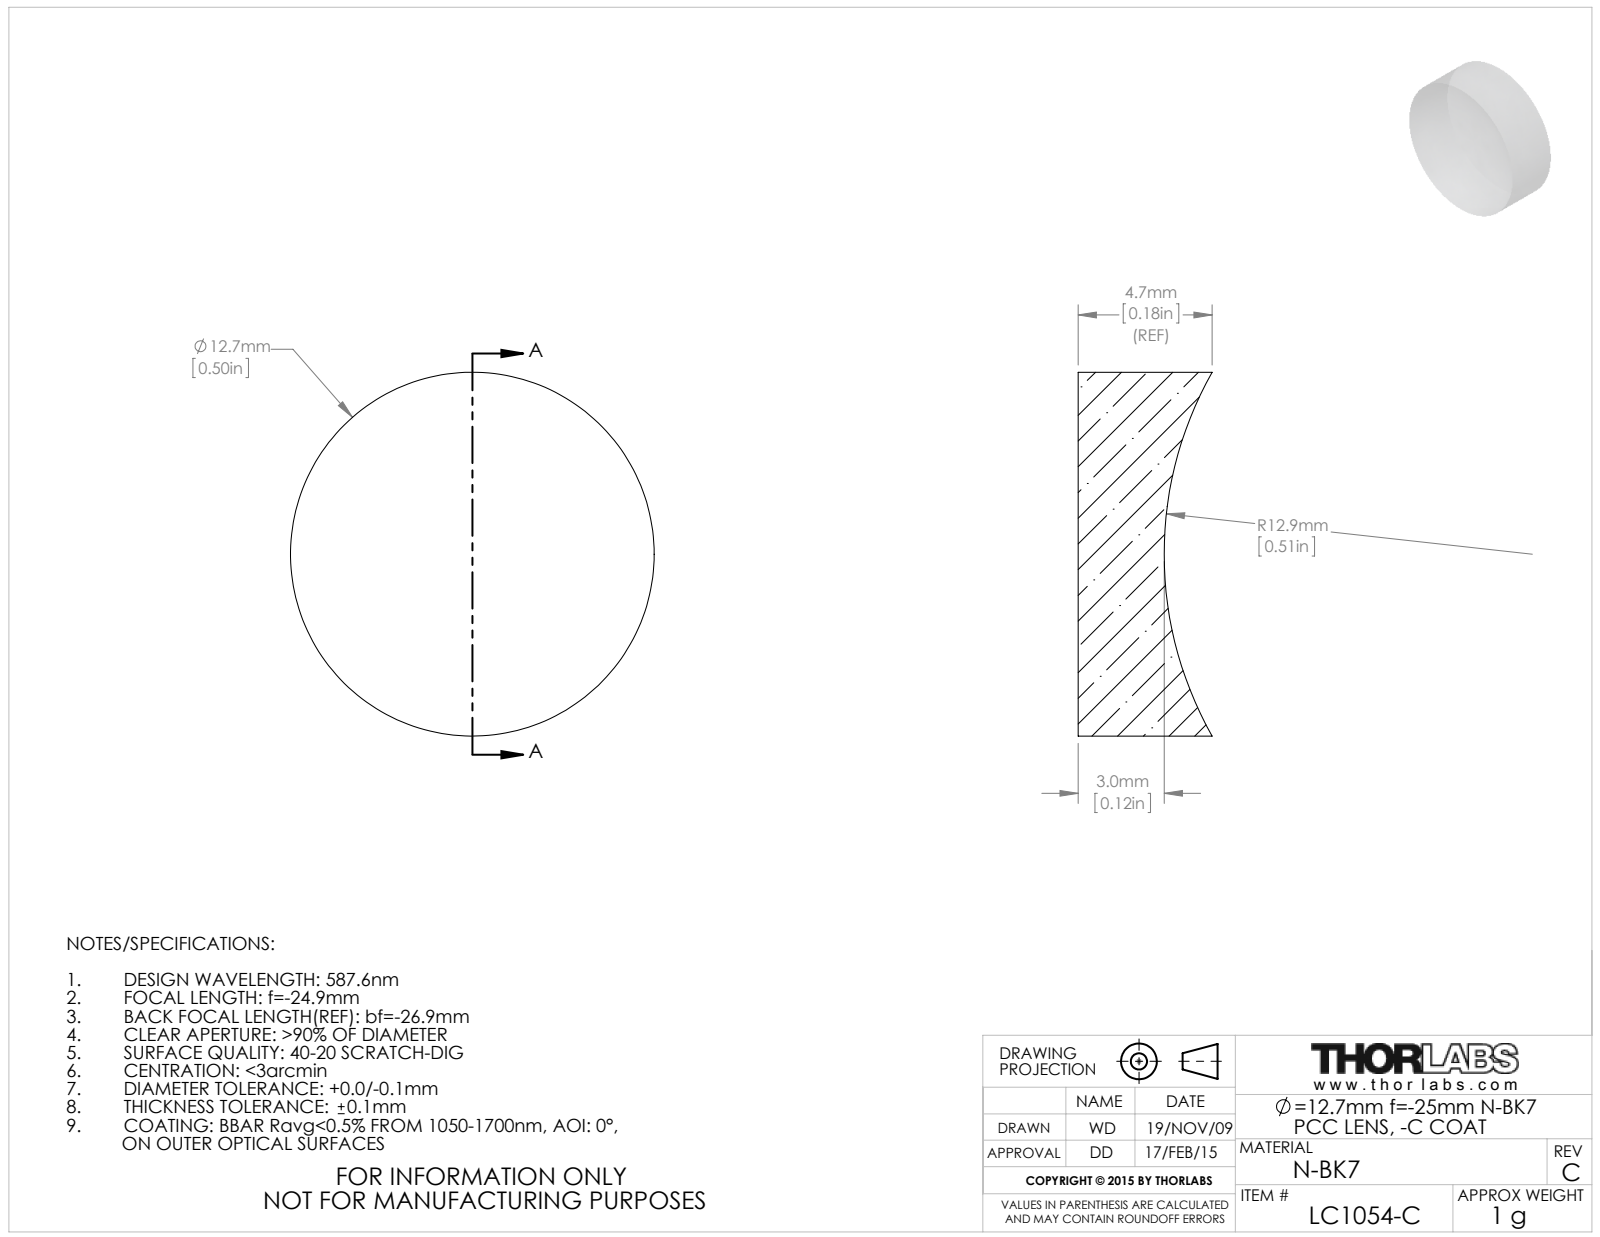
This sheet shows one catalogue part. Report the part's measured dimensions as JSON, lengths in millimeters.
{"part_name": "4801-E0W", "step_written_by": "SolidWorks 2009 (AUTOMOTIVE_DESIGN)", "units": "millimeters", "bodies": {"solids": 1, "faces": 5, "planar": 1, "cylindrical": 2, "other": 2}, "overall_size": [12.7, 12.7, 4.68], "volume_mm3": 484, "surface_area_mm2": 449, "round_bosses_or_shafts": [[12.7, 1]]}
